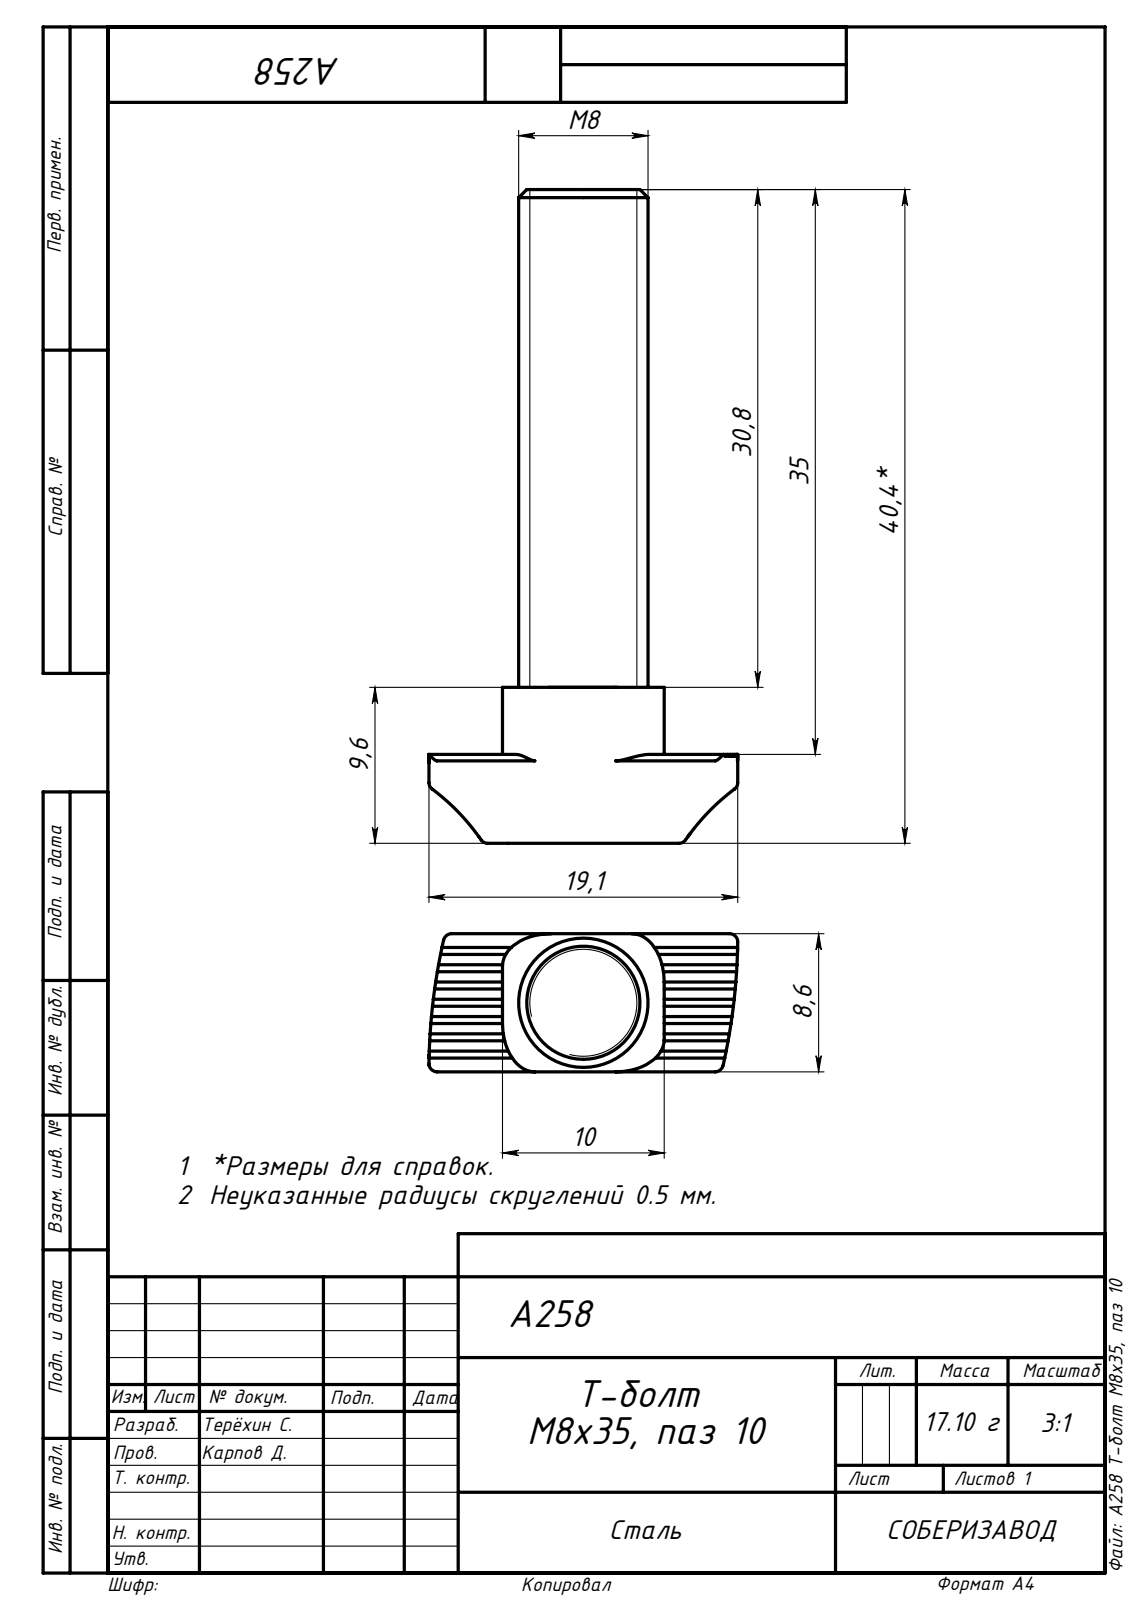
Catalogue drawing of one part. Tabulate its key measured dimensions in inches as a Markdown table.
| quantity | value |
| --- | --- |
| part name | A258 Т-болт М8х35, паз 10 |
| STEP written by | SolidWorks 2020 (AUTOMOTIVE_DESIGN) |
| units | inches |
| bodies | 1 solid, 77 faces (27 planar, 26 cylindrical, 24 other) |
| overall size | 1.593 × 0.752 × 0.337 |
| volume | 0.161 in³ |
| surface area | 2.23 in² |
| round bosses / shafts (diameter × count) | 0.315 × 1 |
| partial cylindrical surfaces (radius × count) | 0.022 × 8, 0.02 × 6, 1.459 × 2 |
| main face-to-face distances | 0.337, 1.593, 0.38, 1.213, 0.213, 0.167, 1.38, 0.394, 0.178, 0.572 |
